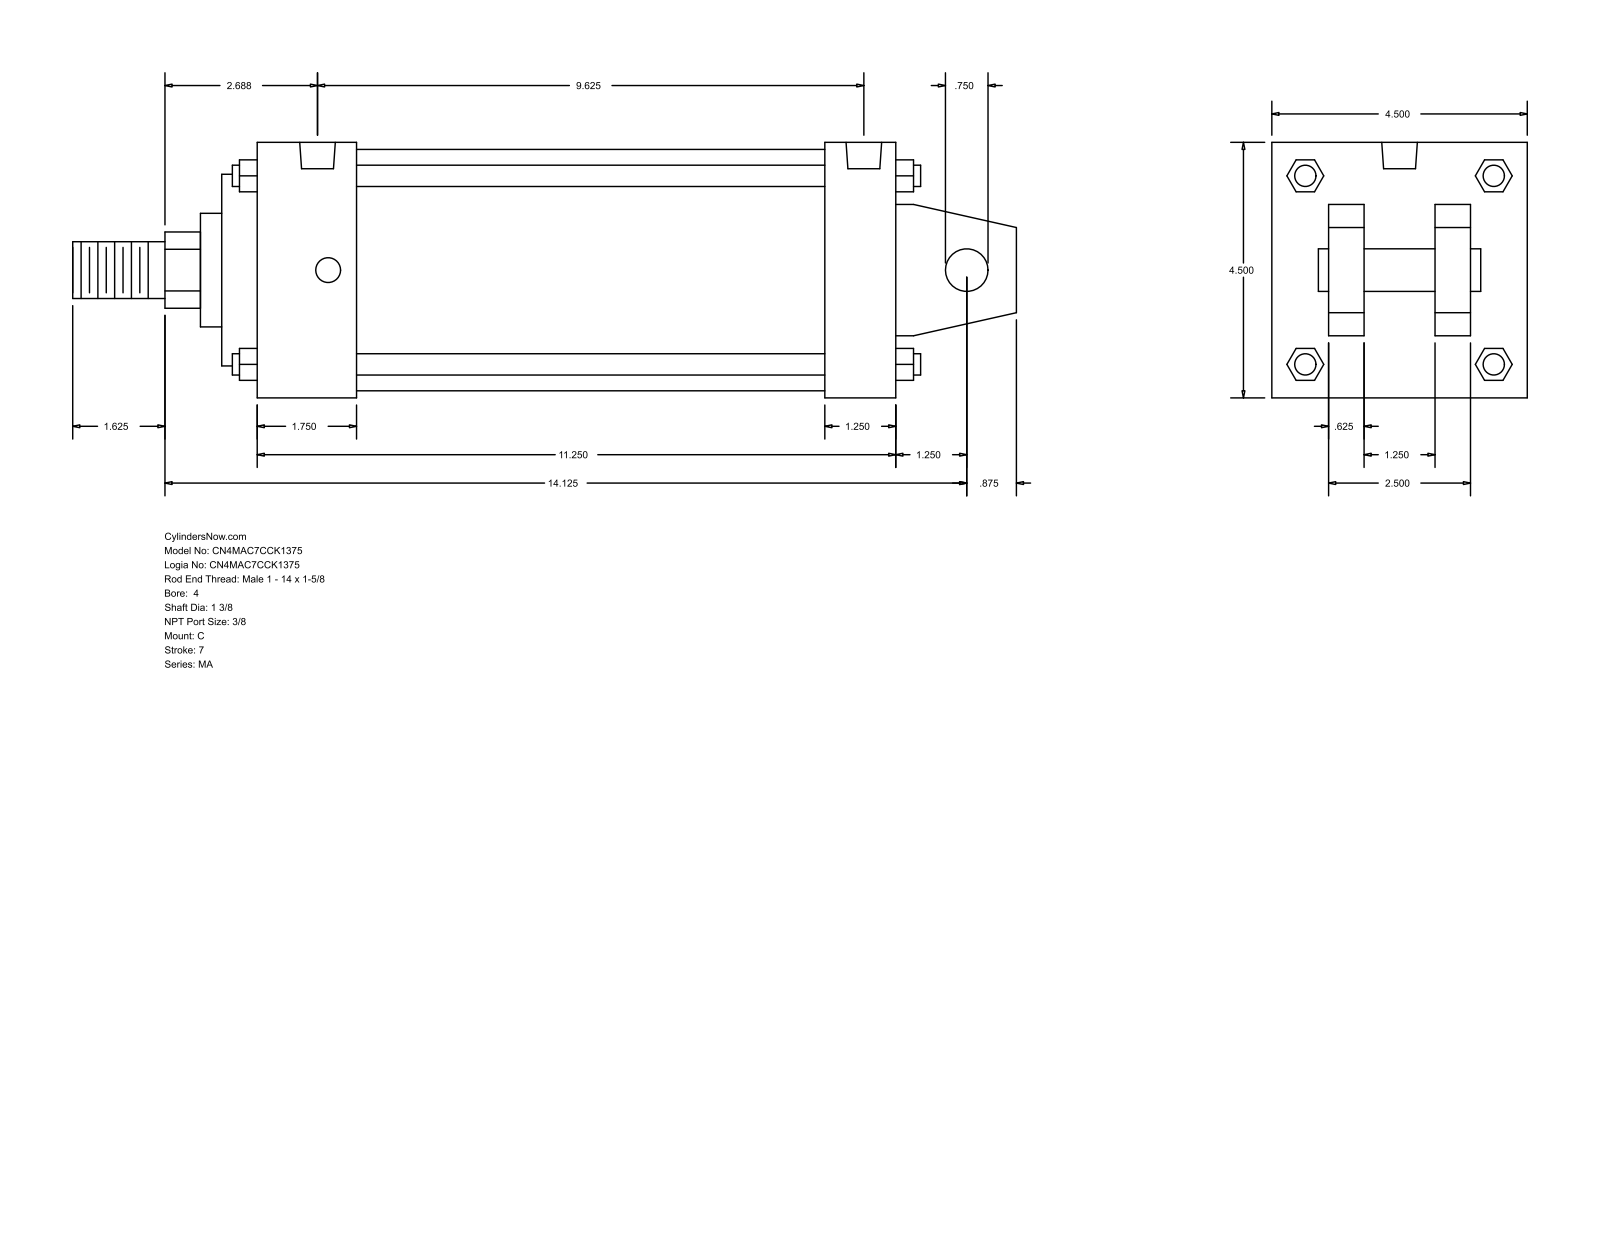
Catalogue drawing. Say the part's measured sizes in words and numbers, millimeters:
The part is named "MA_C__0400_1.375". Its 3-D file was written by "GSSL Pune (CONFIG_CONTROL_DESIGN)". It is 0 solids with 141 faces: 109 planar, 32 cylindrical and 0 other. Overall it measures 422.27 by 114.3 by 114.3 millimeters. Round holes: 4 of diameter 11.11, 2 of diameter 15.93. Round bosses or shafts: 4 of diameter 9.53, 1 of diameter 107.95, 1 of diameter 85.72, 1 of diameter 50.8, 1 of diameter 34.92, 1 of diameter 25.4, 1 of diameter 19.05. Partial cylindrical surfaces (rounded edges, fillets, slot ends): 1 of radius 17.06. The main face-to-face distances are 114.3, 15.87, 285.75, 73.03, 41.27, 25.4, 88.9, 47.63, 301.62, 269.87. The hole center spacings are 234.95, 4.76, 4.77, 239.71, 239.72, 244.48.
